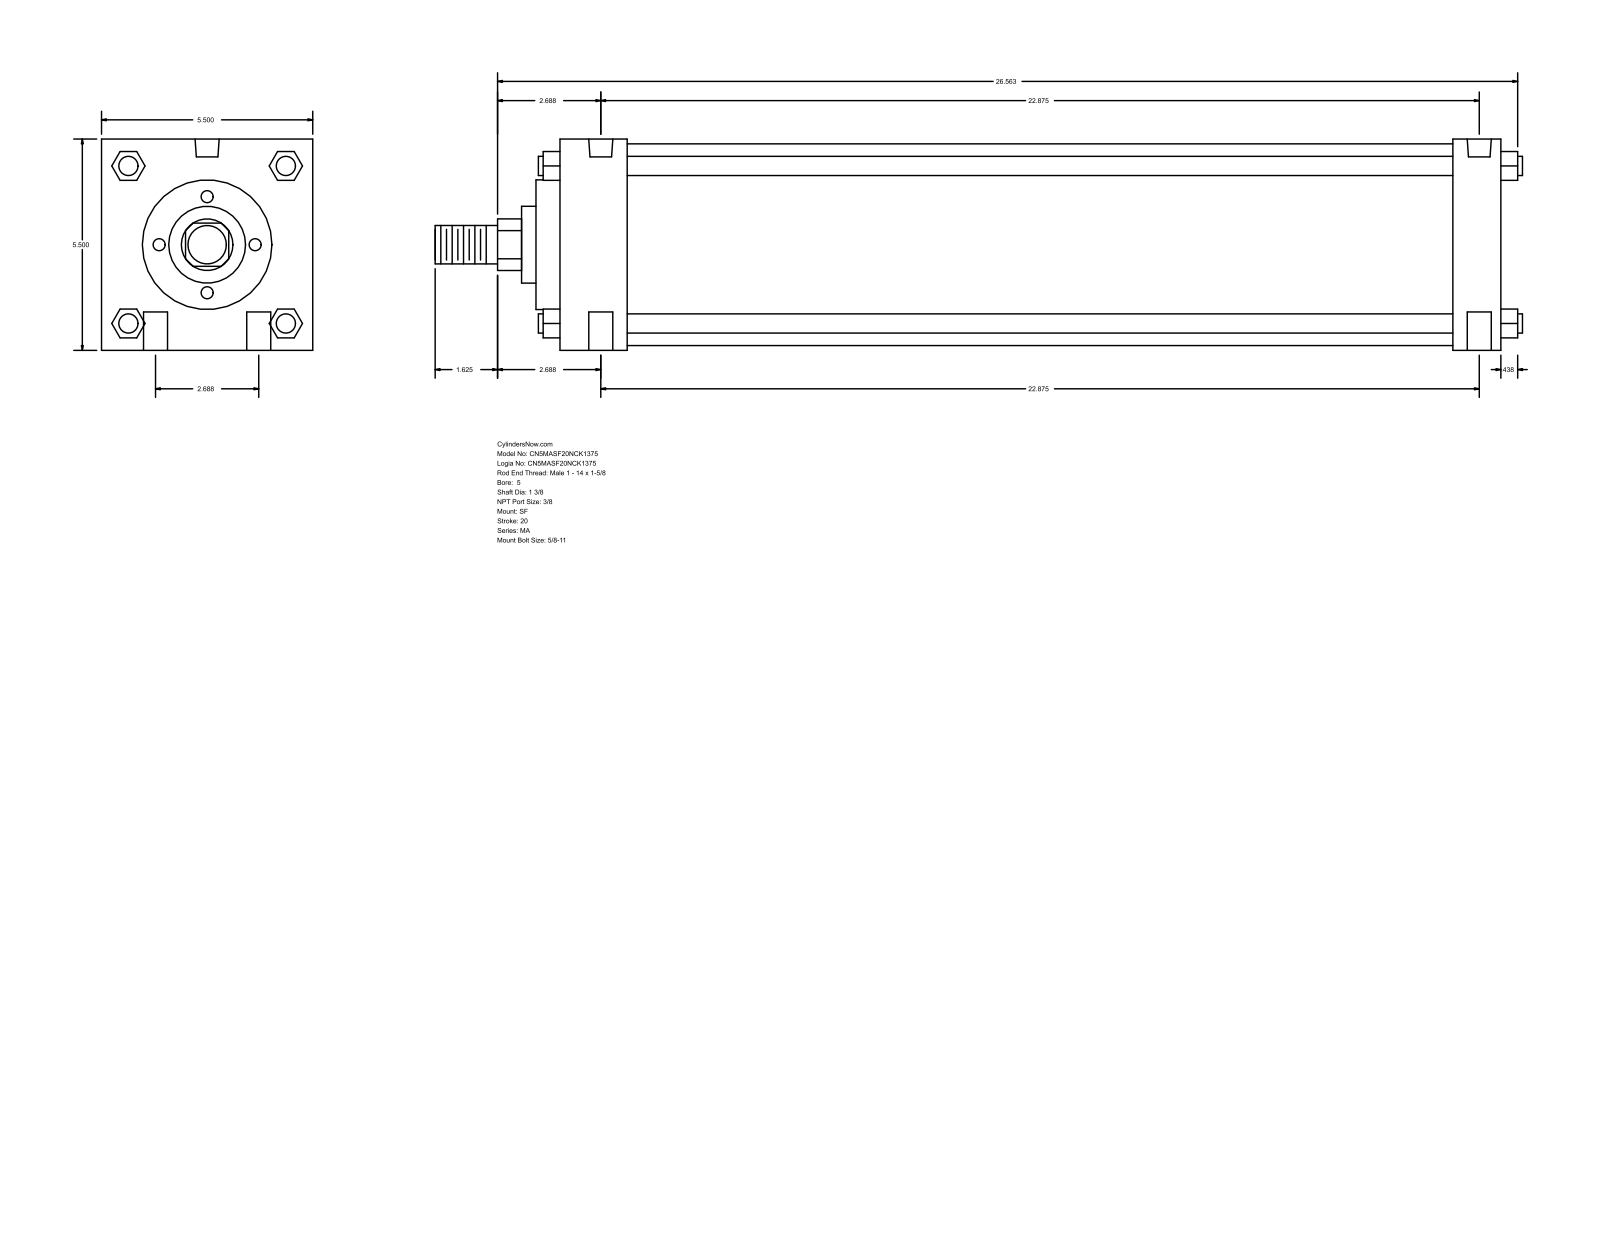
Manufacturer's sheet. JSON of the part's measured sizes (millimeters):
{"part_name": "MA_SF__0500_1.375", "step_written_by": "GSSL Pune (CONFIG_CONTROL_DESIGN)", "units": "millimeters", "bodies": {"solids": 0, "faces": 126, "planar": 95, "cylindrical": 31, "other": 0}, "overall_size": [719.14, 139.7, 139.7], "round_holes": [[15.88, 4], [11.11, 2], [15.93, 2]], "round_bosses_or_shafts": [[12.7, 4], [133.35, 1], [85.72, 1], [50.8, 1], [34.92, 1], [25.4, 1]], "partial_cylinders_radius": [[17.06, 1]], "face_to_face_distances": [139.7, 622.31, 44.45, 590.56, 546.11, 577.86, 31.75, 15.87, 60.32, 606.43], "hole_center_spacings": [34.13, 582.03, 581.03, 68.26, 585.03, 571.49]}
